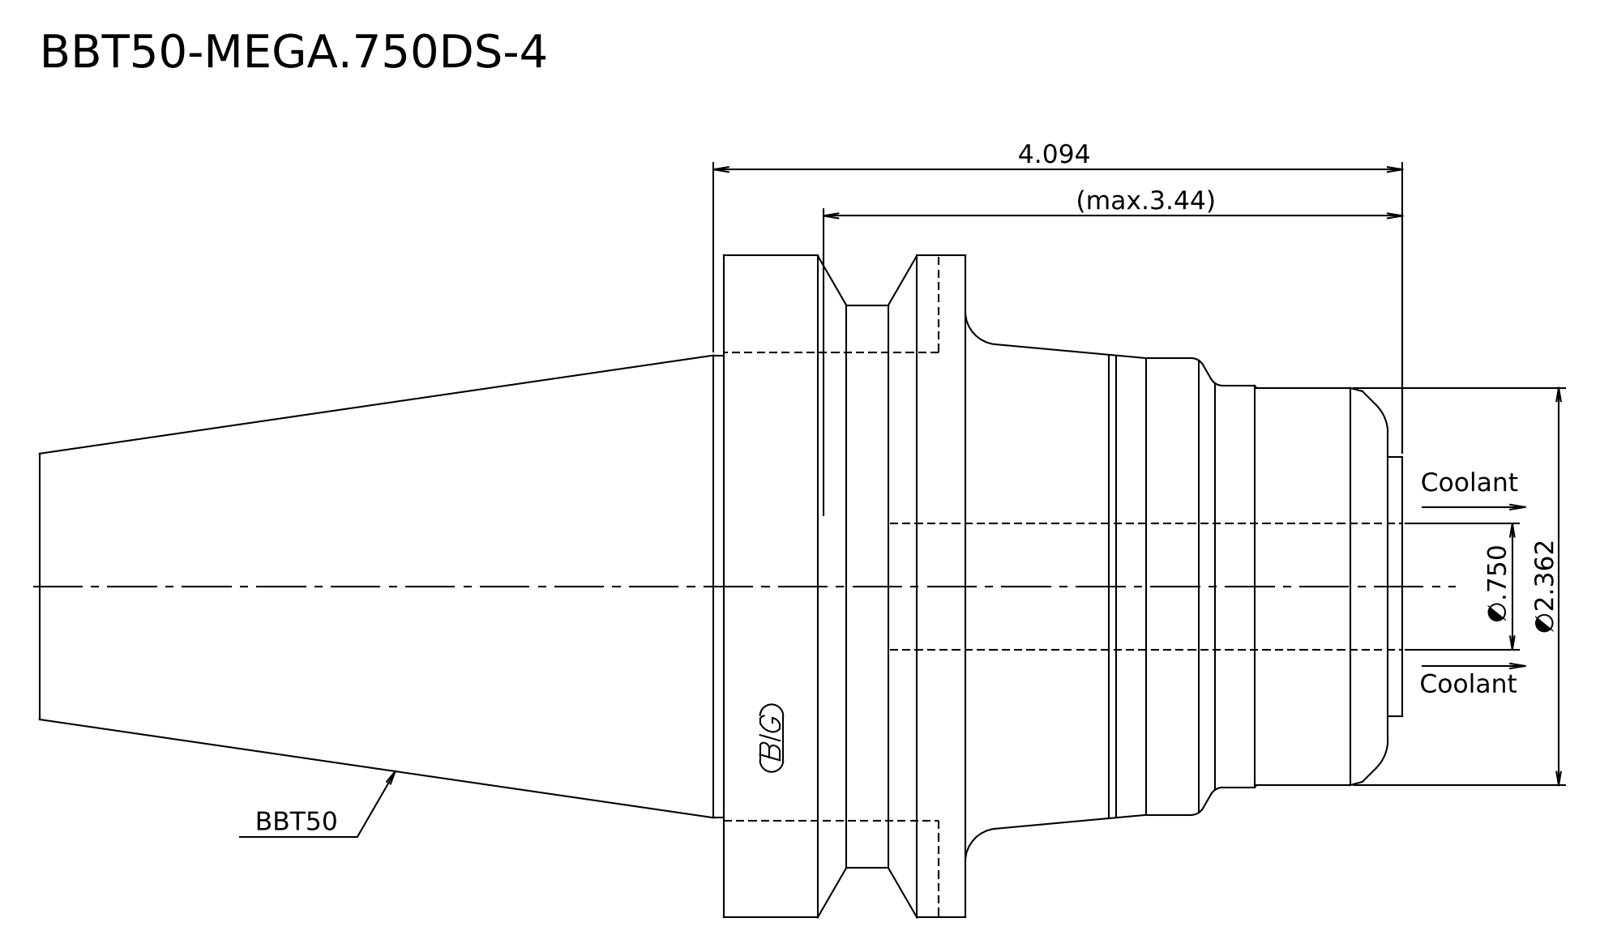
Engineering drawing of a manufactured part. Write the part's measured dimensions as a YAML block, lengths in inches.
step_written_by: "Kubotek KeyCreator 2011 V10.0.2 (22737) (automotive_design)"
units: inches
bodies: {solids: 1, faces: 22, planar: 5, cylindrical: 8, other: 9}
overall_size: [8.102, 3.937, 3.937]
volume: 45.28
surface_area: 87.22
round_bosses_or_shafts:
  - {diameter: 3.937, count: 1}
  - {diameter: 3.346, count: 1}
  - {diameter: 2.75, count: 1}
  - {diameter: 2.717, count: 1}
  - {diameter: 2.39, count: 1}
  - {diameter: 2.362, count: 1}
  - {diameter: 1.545, count: 1}
face_to_face_distances: [1.437, 5.504, 4.067, 2.598, 4.035, 8.102, 0.087, 2.512, 3.949, 8.016]
